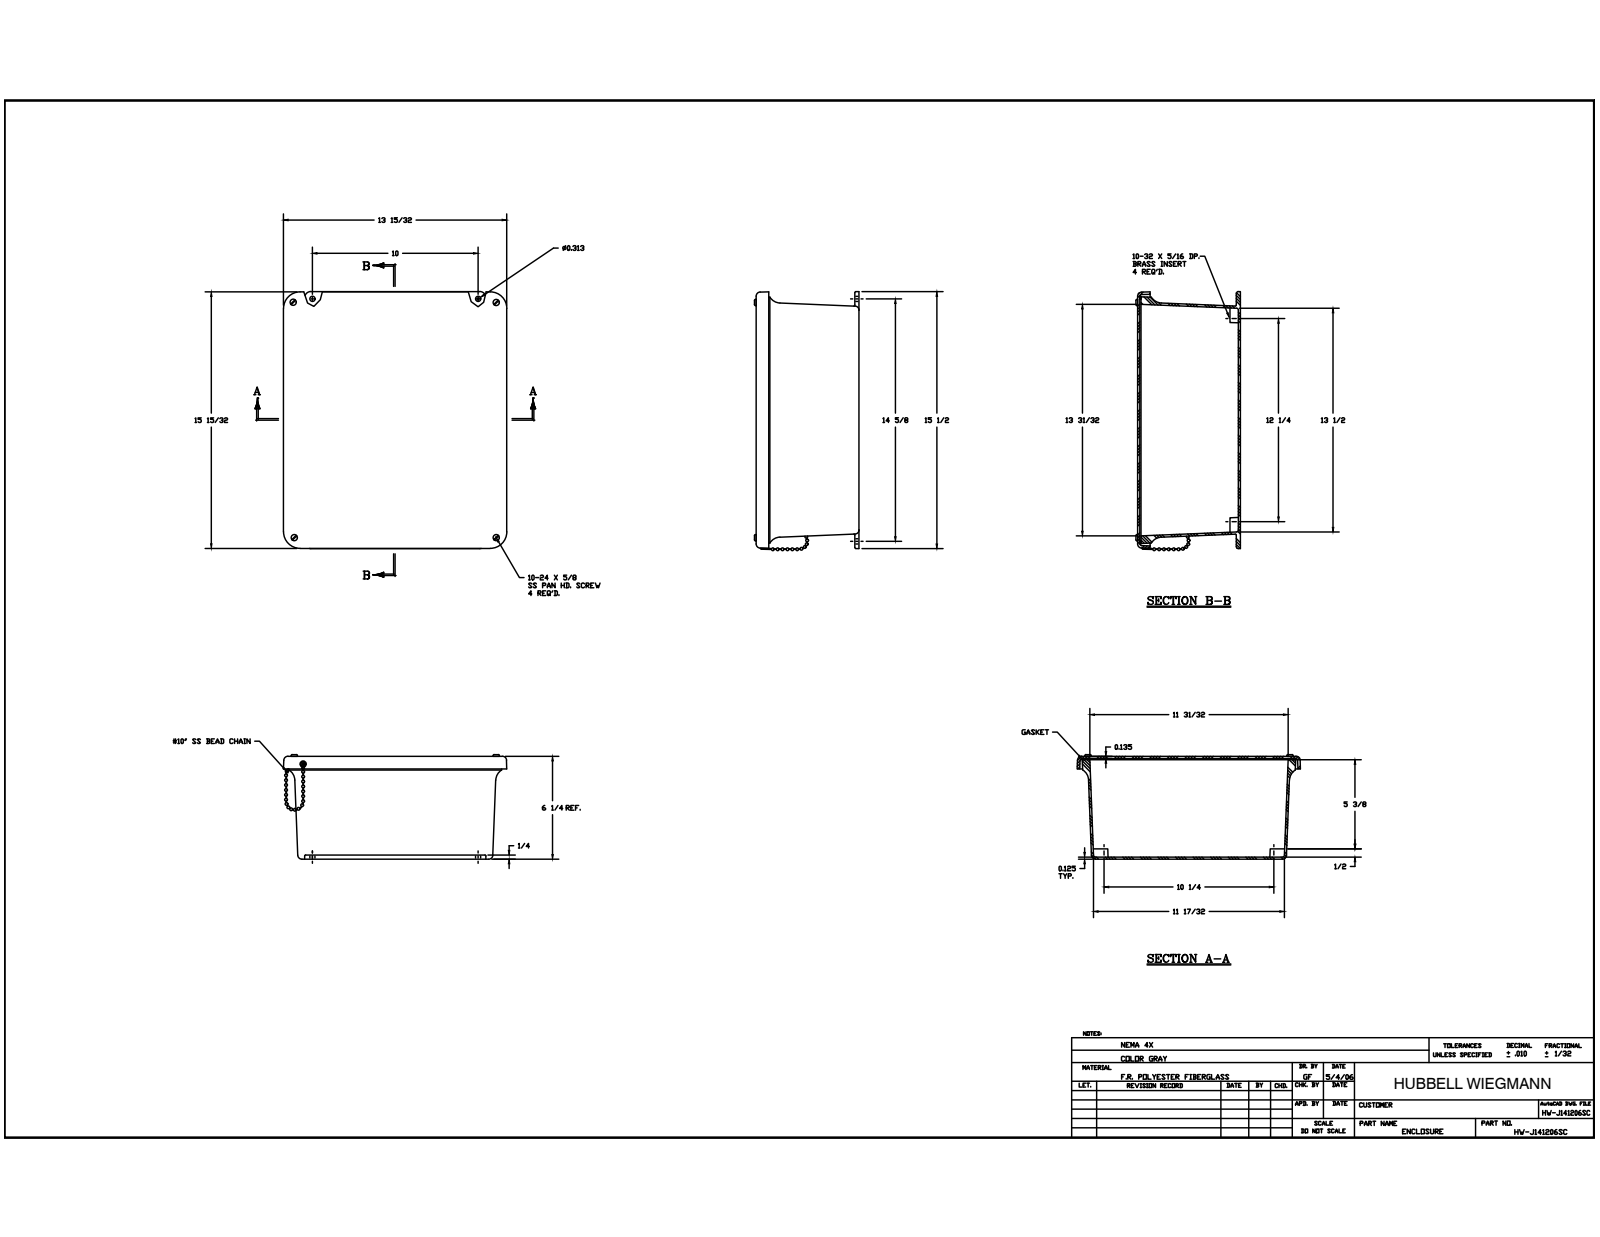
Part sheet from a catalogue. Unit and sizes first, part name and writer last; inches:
Units: inches
Overall size (bounding box): 16.119 × 13.767 × 6.33
Round holes (diameter × count): ⌀0.152 ×8, ⌀0.14 ×6, ⌀0.145 ×4, ⌀0.156 ×4, ⌀0.218 ×4, ⌀0.187 ×2, ⌀0.126 ×1
Round bosses / shafts (diameter × count): ⌀0.27 ×8, ⌀0.19 ×4, ⌀0.156 ×4, ⌀0.375 ×2, ⌀0.25 ×2, ⌀0.125 ×2, ⌀0.283 ×1
Partial cylindrical surfaces — rounded edges, fillets, slot ends (radius × count): R0.031 ×20, R0.125 ×12, R0.25 ×12, R0.2 ×8, R0.375 ×4, R0.75 ×4, R0.01 ×2, R0.063 ×2
Main face-to-face distances: 0.125, 0.135, 6.064, 6.199, 5.939, 6.074, 0.125, 0.33, 0.064, 6
Hole centre spacings: 1.37, 11.26, 13.254, 17.337, 3.25, 6.5, 10.25, 12.187
Volume: 112.4 in³ · Surface area: 1 535 in²
Bodies: 21 solids, 874 faces (191 planar, 295 cylindrical, 388 other)
Part name (STEP PRODUCT): J1412W_1; RMINS45821P_183; RMINS45821P_184; RMINS45821P_185 (+8 more)
STEP written by: Autodesk Inventor 2014 (AUTOMOTIVE_DESIGN)
